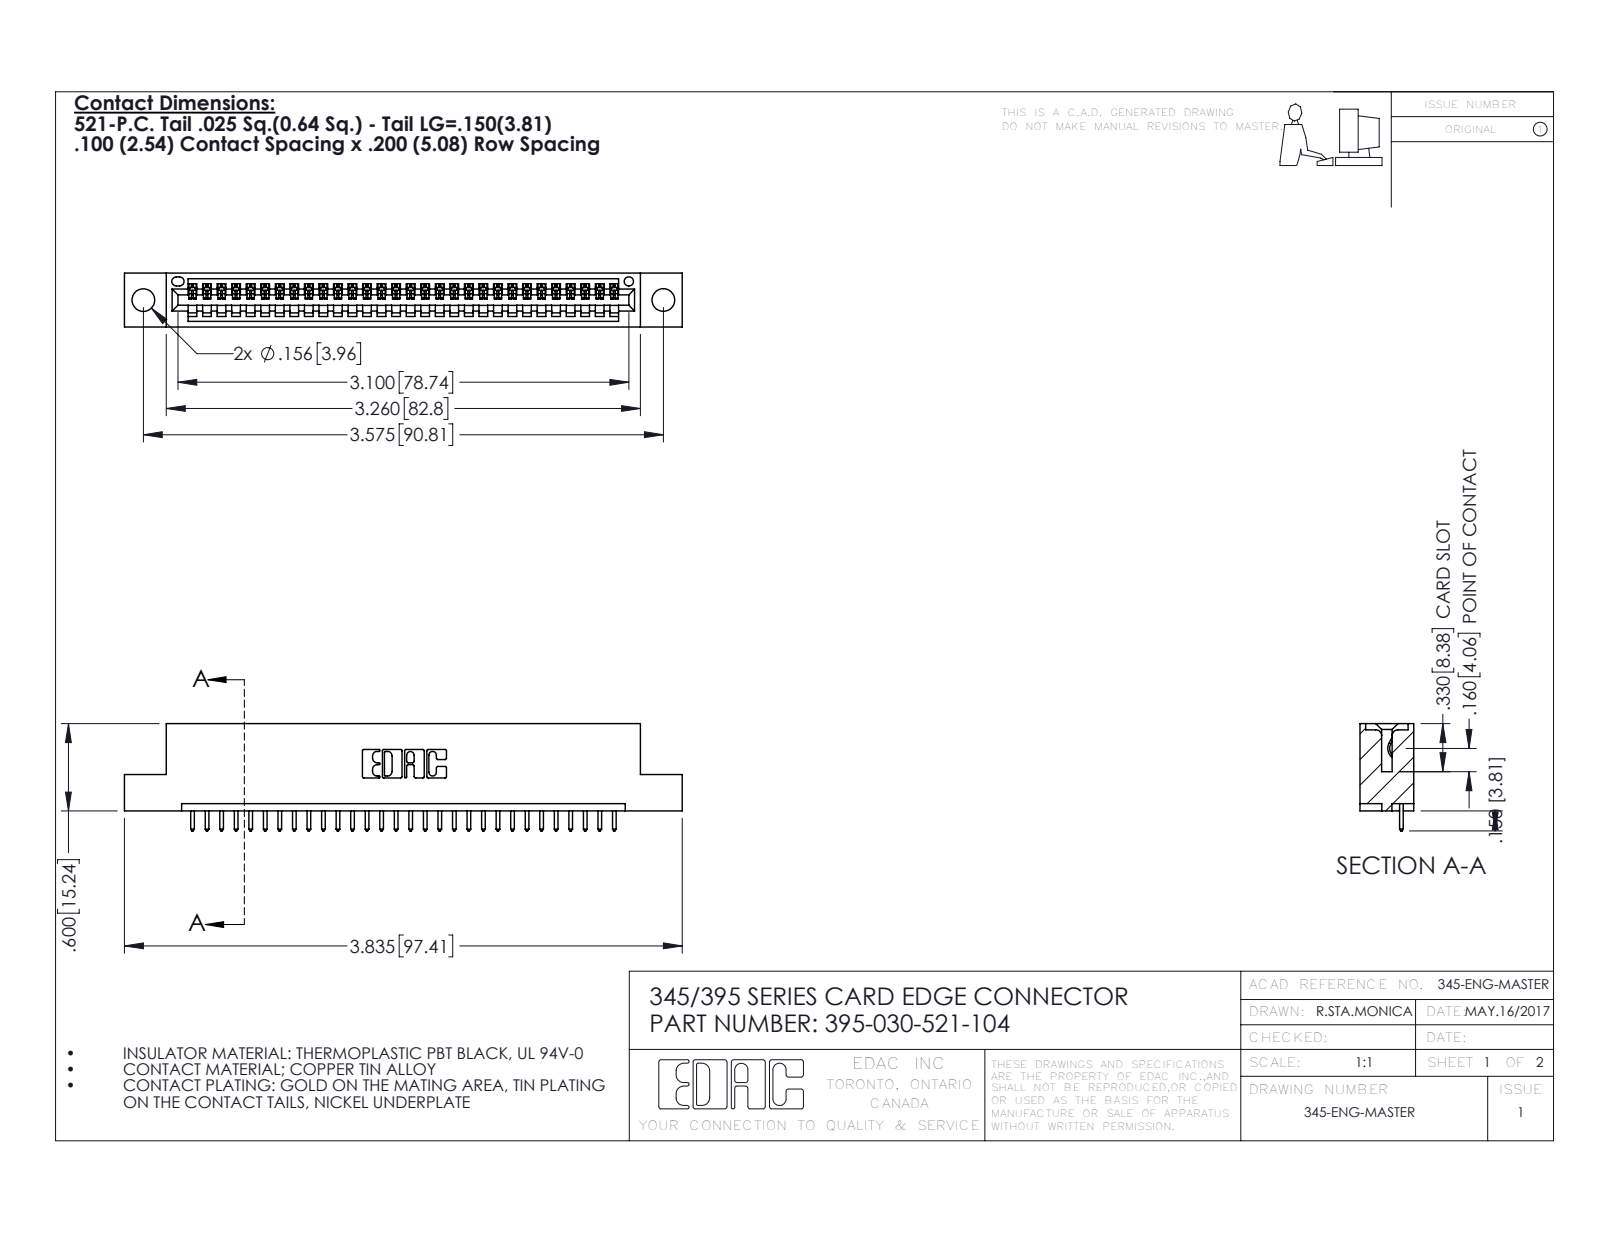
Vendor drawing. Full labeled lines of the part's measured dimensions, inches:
Part name (STEP PRODUCT): 395-030-521-104; 345 Part_Flush Mounting Lugs - 0.156 Dia-TH; 345-292-001_345-293-121
STEP written by: SolidWorks 2016 (CONFIG_CONTROL_DESIGN)
Units: inches
Bodies: 31 solids, 1866 faces (1280 planar, 586 cylindrical, 0 other)
Overall size (bounding box): 3.835 × 0.737 × 0.37
Volume: 0.548 in³ · Surface area: 17.43 in²
Round holes (diameter × count): ⌀0.156 ×2, ⌀0.064 ×1
Partial cylindrical surfaces — rounded edges, fillets, slot ends (radius × count): R0.006 ×60, R0.01 ×60, R0.01 ×22, R0.007 ×6, R0.031 ×6, R0.026 ×3, R0.031 ×2, R0.04 ×2
Main face-to-face distances: 0.298, 0.072, 0.37, 0.2, 0.098, 0.272, 0.025, 0.225, 0.149, 0.072
Hole centre spacings: 0.27, 3.34, 3.575
